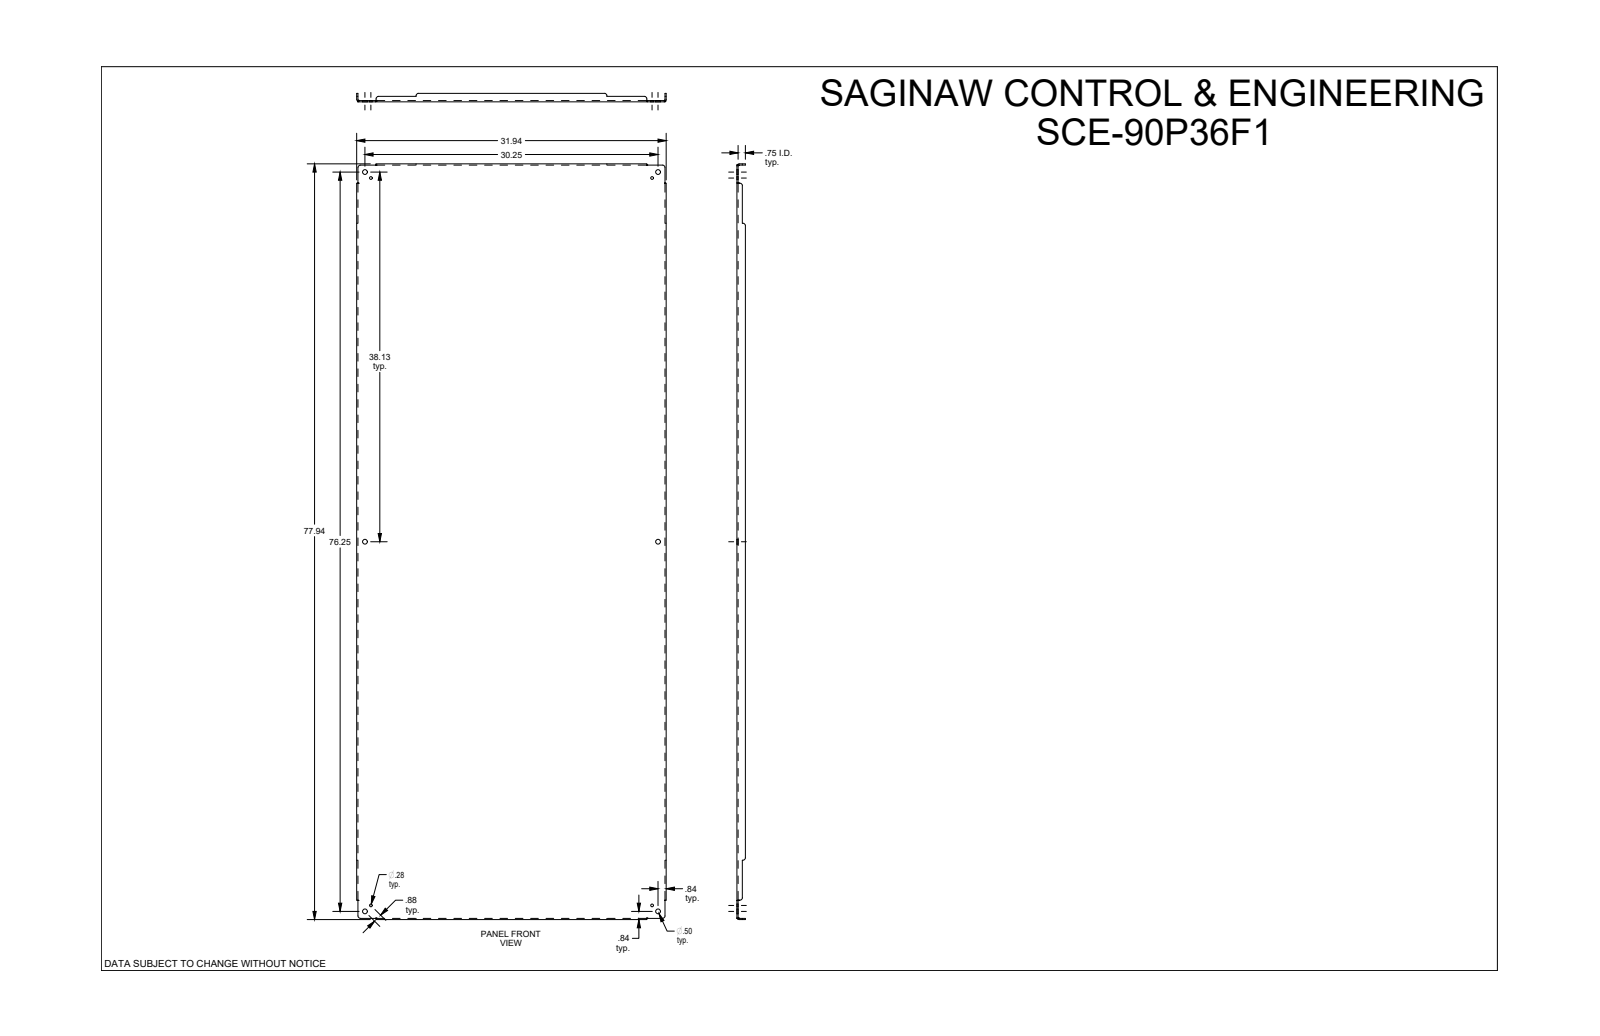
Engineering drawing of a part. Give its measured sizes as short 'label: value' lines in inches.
name: SCE-90P36F1
written by: SolidWorks 2019 (AUTOMOTIVE_DESIGN)
unit: in
bodies: 1 solid, 108 faces (46 planar, 38 cylindrical, 24 other)
size: 77.938 × 31.938 × 0.875
volume: 326.6 in³; area: 5 255 in²
holes: 6× ⌀0.5, 4× ⌀0.281
rounds: 12× R0.25, 4× R0.112, 4× R0.237
face distances: 0.125, 0.125, 31.813, 31.687, 31.938, 77.813, 0.75, 0.875, 77.687, 77.938
hole spacings: 0.875, 29.637, 37.511, 38.125, 47.799, 48.668, 75.634, 81.229
